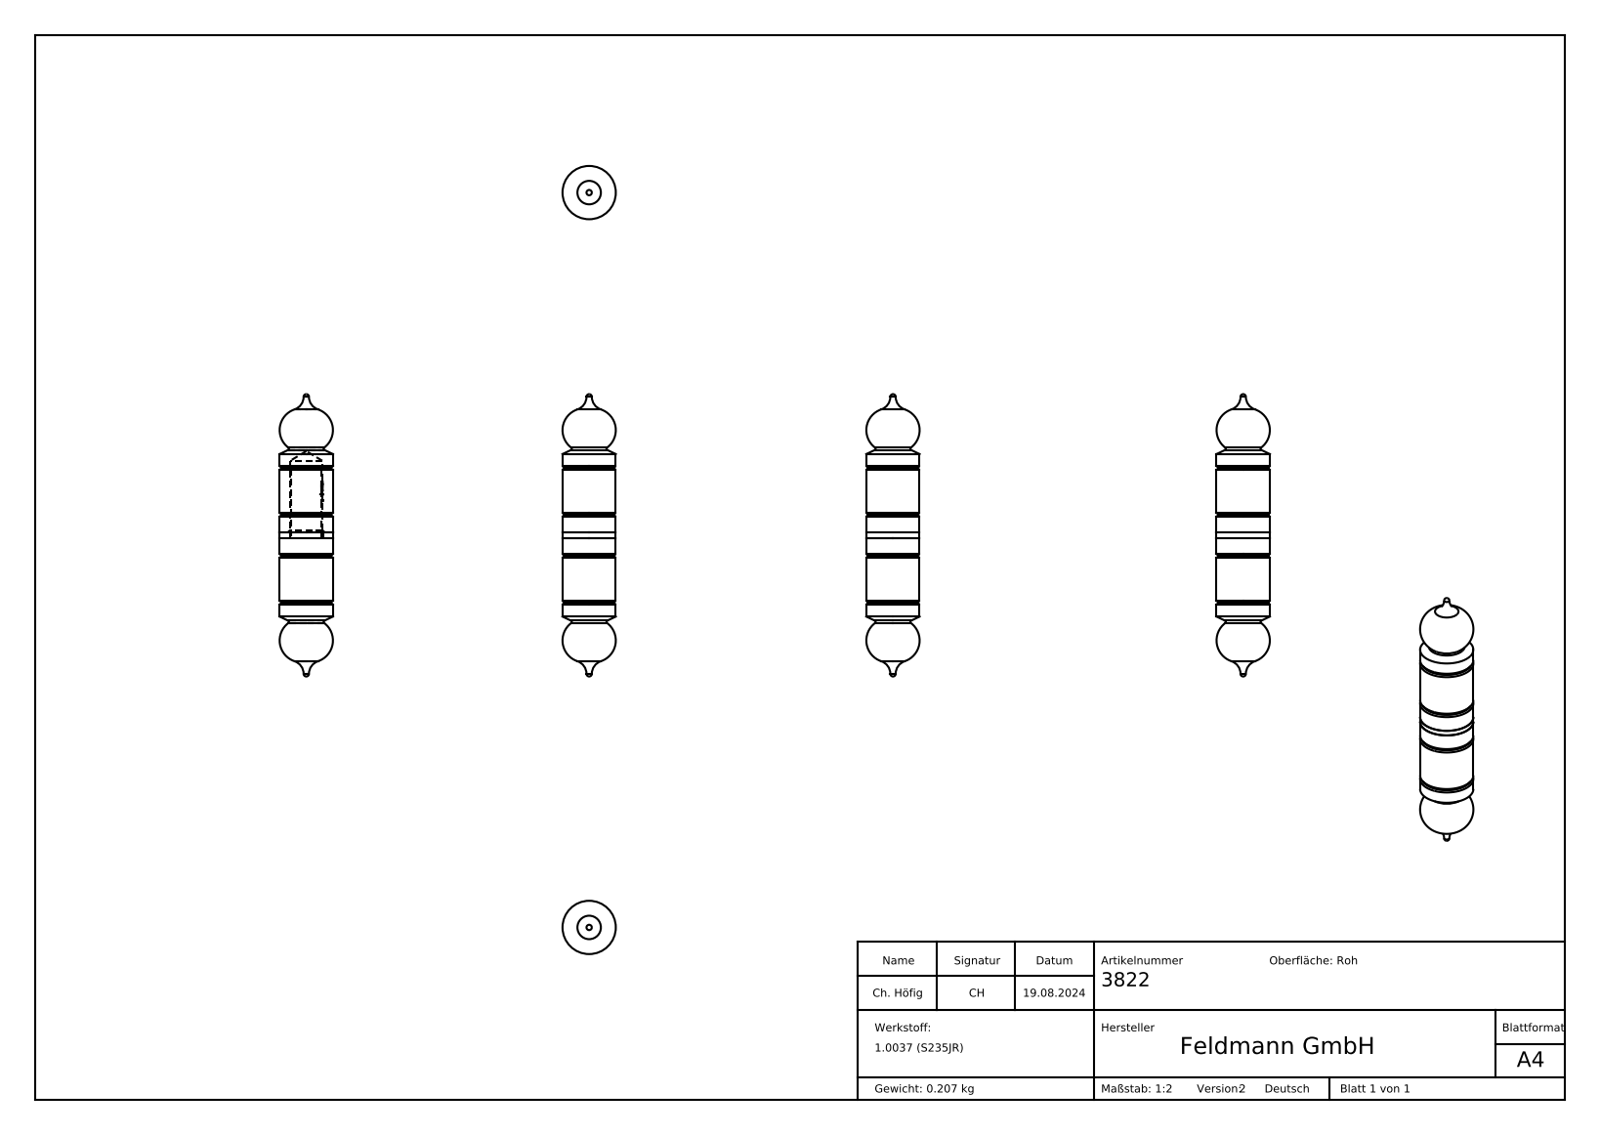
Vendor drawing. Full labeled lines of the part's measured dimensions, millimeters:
Part name (STEP PRODUCT): 382X und 382X-VA Teil1-3_3822 Teil3; 382X und 382X-VA Teil1-3_3822 Teil2; 3822 - Kopie; 382X und 382X-VA Teil1-3_3822 Teil1
STEP written by: SolidWorks 2018 (CONFIG_CONTROL_DESIGN)
Units: millimetres
Bodies: 3 solids, 260 faces (96 planar, 32 cylindrical, 132 other)
Overall size (bounding box): 106 × 20 × 20
Volume: 26 451 mm³ · Surface area: 9 521 mm²
Round holes (diameter × count): ⌀12 ×1, ⌀12.5 ×1
Round bosses / shafts (diameter × count): ⌀20 ×1, ⌀19 ×1, ⌀11.5 ×1
Partial cylindrical surfaces — rounded edges, fillets, slot ends (radius × count): R6.1 ×1
Main face-to-face distances: 2, 27, 25, 0.31, 0.44, 0.32, 3.12, 2.49, 2.06, 5.5
